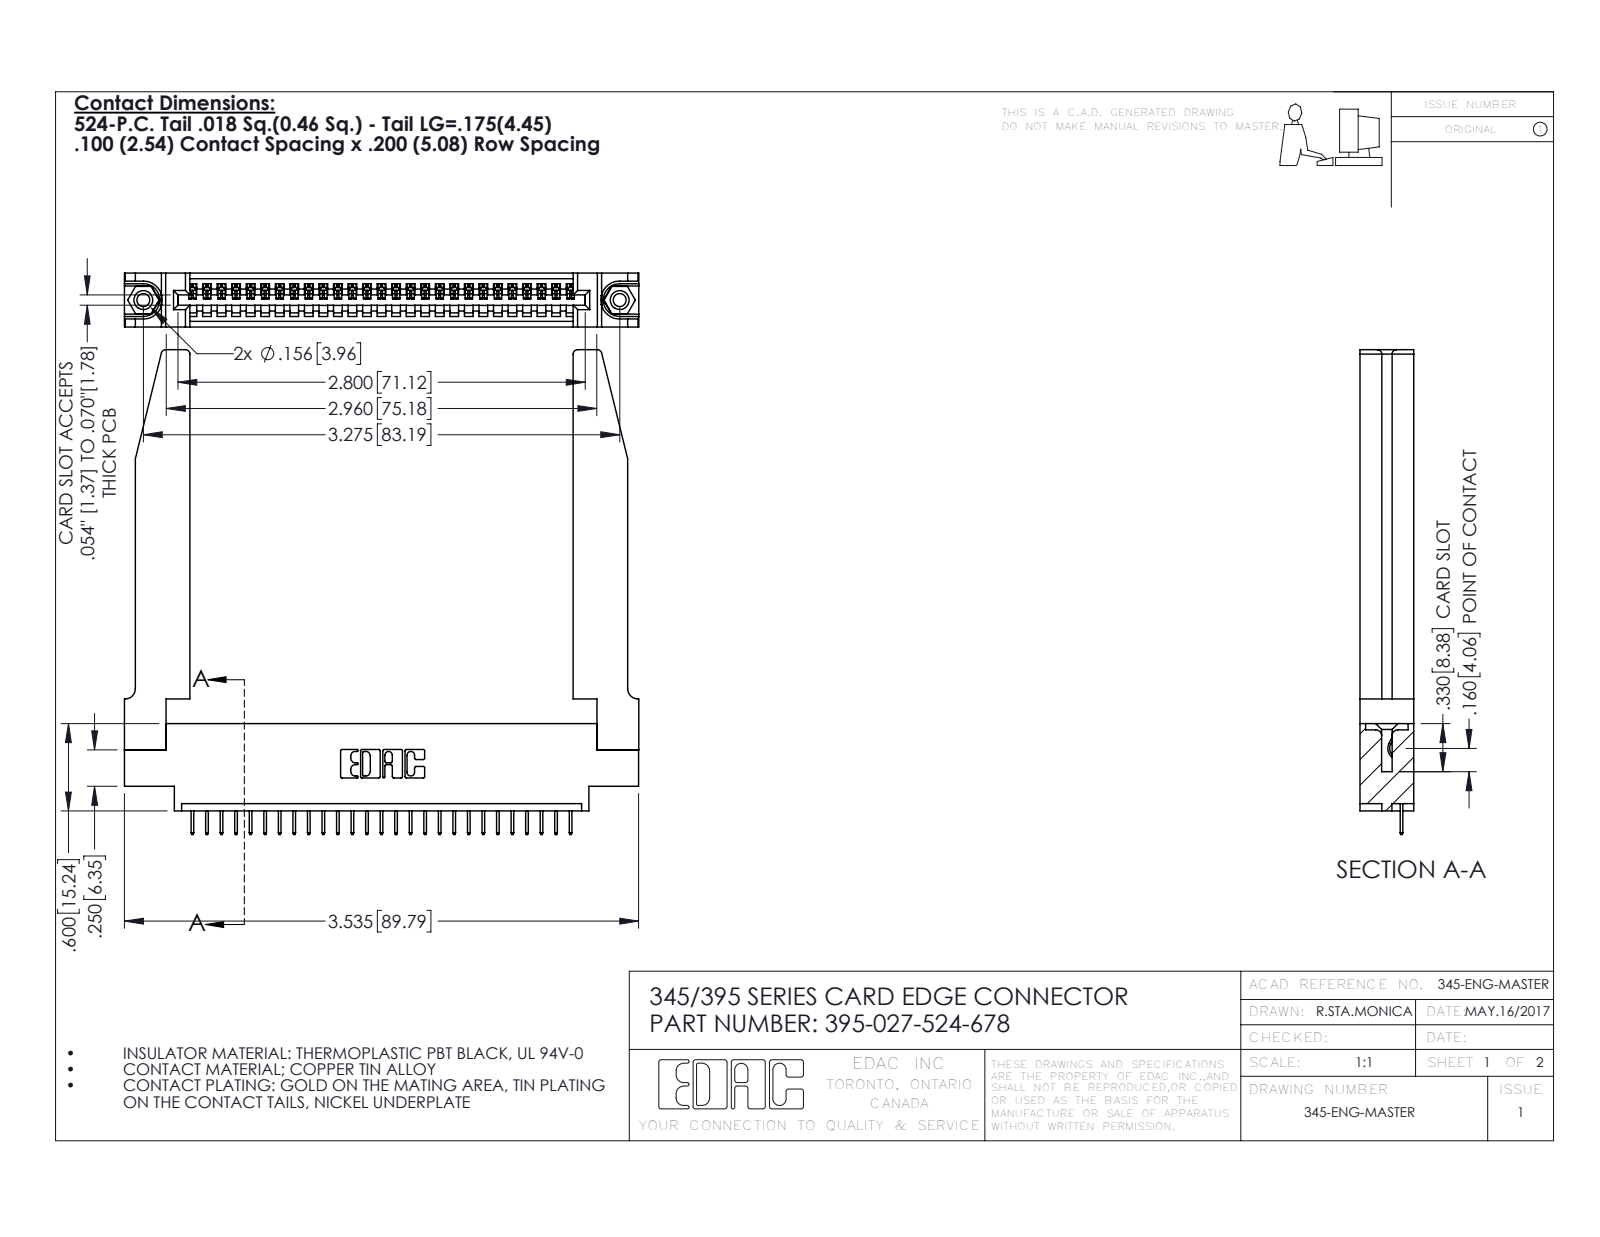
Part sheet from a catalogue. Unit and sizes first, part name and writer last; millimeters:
Units: millimetres
Overall size (bounding box): 89.8 × 84.6 × 9.4
Round holes (diameter × count): ⌀2.3 ×2, ⌀3.2 ×2, ⌀4 ×2, ⌀1.6 ×1
Round bosses / shafts (diameter × count): ⌀3.9 ×2
Partial cylindrical surfaces — rounded edges, fillets, slot ends (radius × count): R0.2 ×54, R0.3 ×22, R0.8 ×8, R0.2 ×6, R0.8 ×6, R0.7 ×3, R0.8 ×2, R1 ×2
Main face-to-face distances: 9.4, 1.8, 7.6, 2.5, 6.9, 0.6, 5.1, 3.8, 3.8, 5.7
Hole centre spacings: 6.9, 77.2, 83.2
Volume: 16 000 mm³ · Surface area: 17 310 mm²
Bodies: 32 solids, 2038 faces (1468 planar, 518 cylindrical, 52 other)
Part name (STEP PRODUCT): 345-220-078_345-220-078; 345-250-001_345-250-001-102; 395-027-524-678; 345-292-001_345-293-124 (+1 more)
STEP written by: SolidWorks 2016 (CONFIG_CONTROL_DESIGN)
